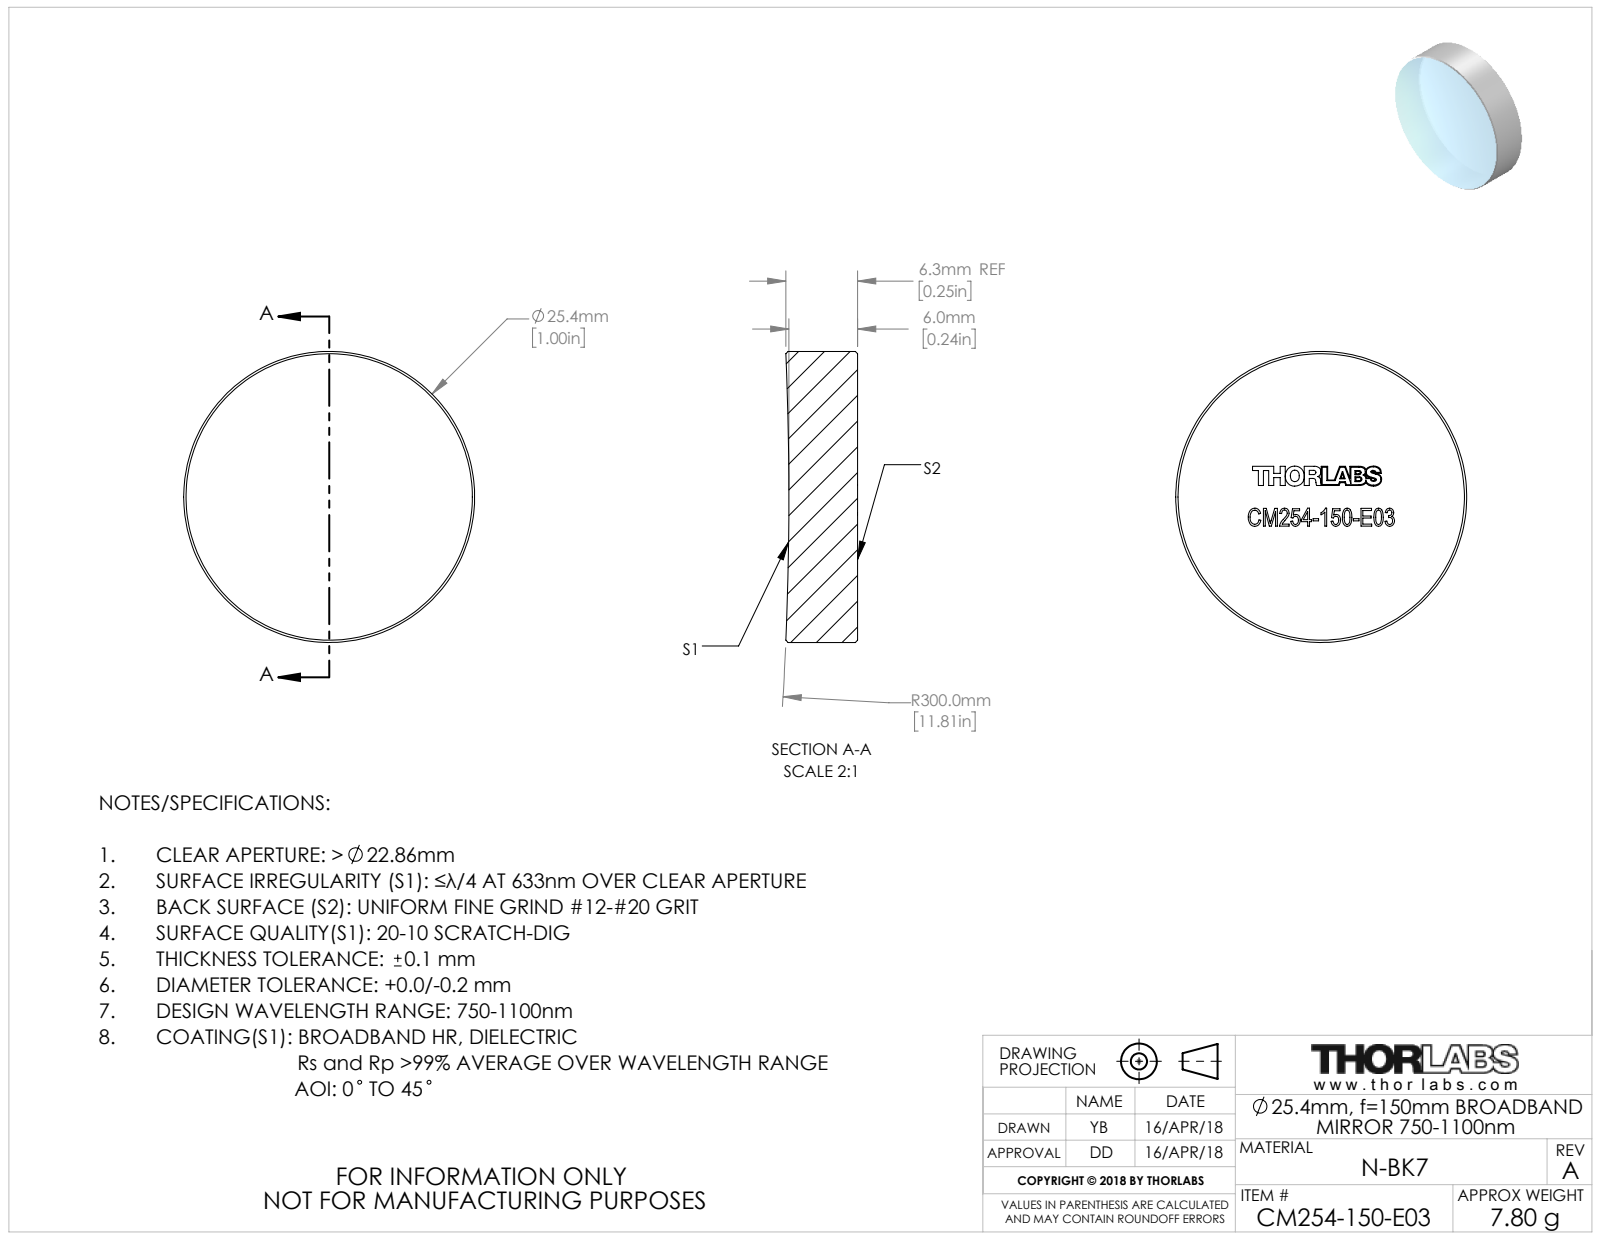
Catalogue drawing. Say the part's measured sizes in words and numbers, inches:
The part is named "TTN153280-E0W". Its 3-D file was written by "SolidWorks 2018 (CONFIG_CONTROL_DESIGN)". It is 1 solid with 40 faces: 32 planar, 2 cylindrical and 6 other. Overall it measures 1 by 1 by 0.246 inches. Its volume is 0.189 cubic inches and its surface area 2.317 square inches. Round bosses or shafts: 1 of diameter 1.
